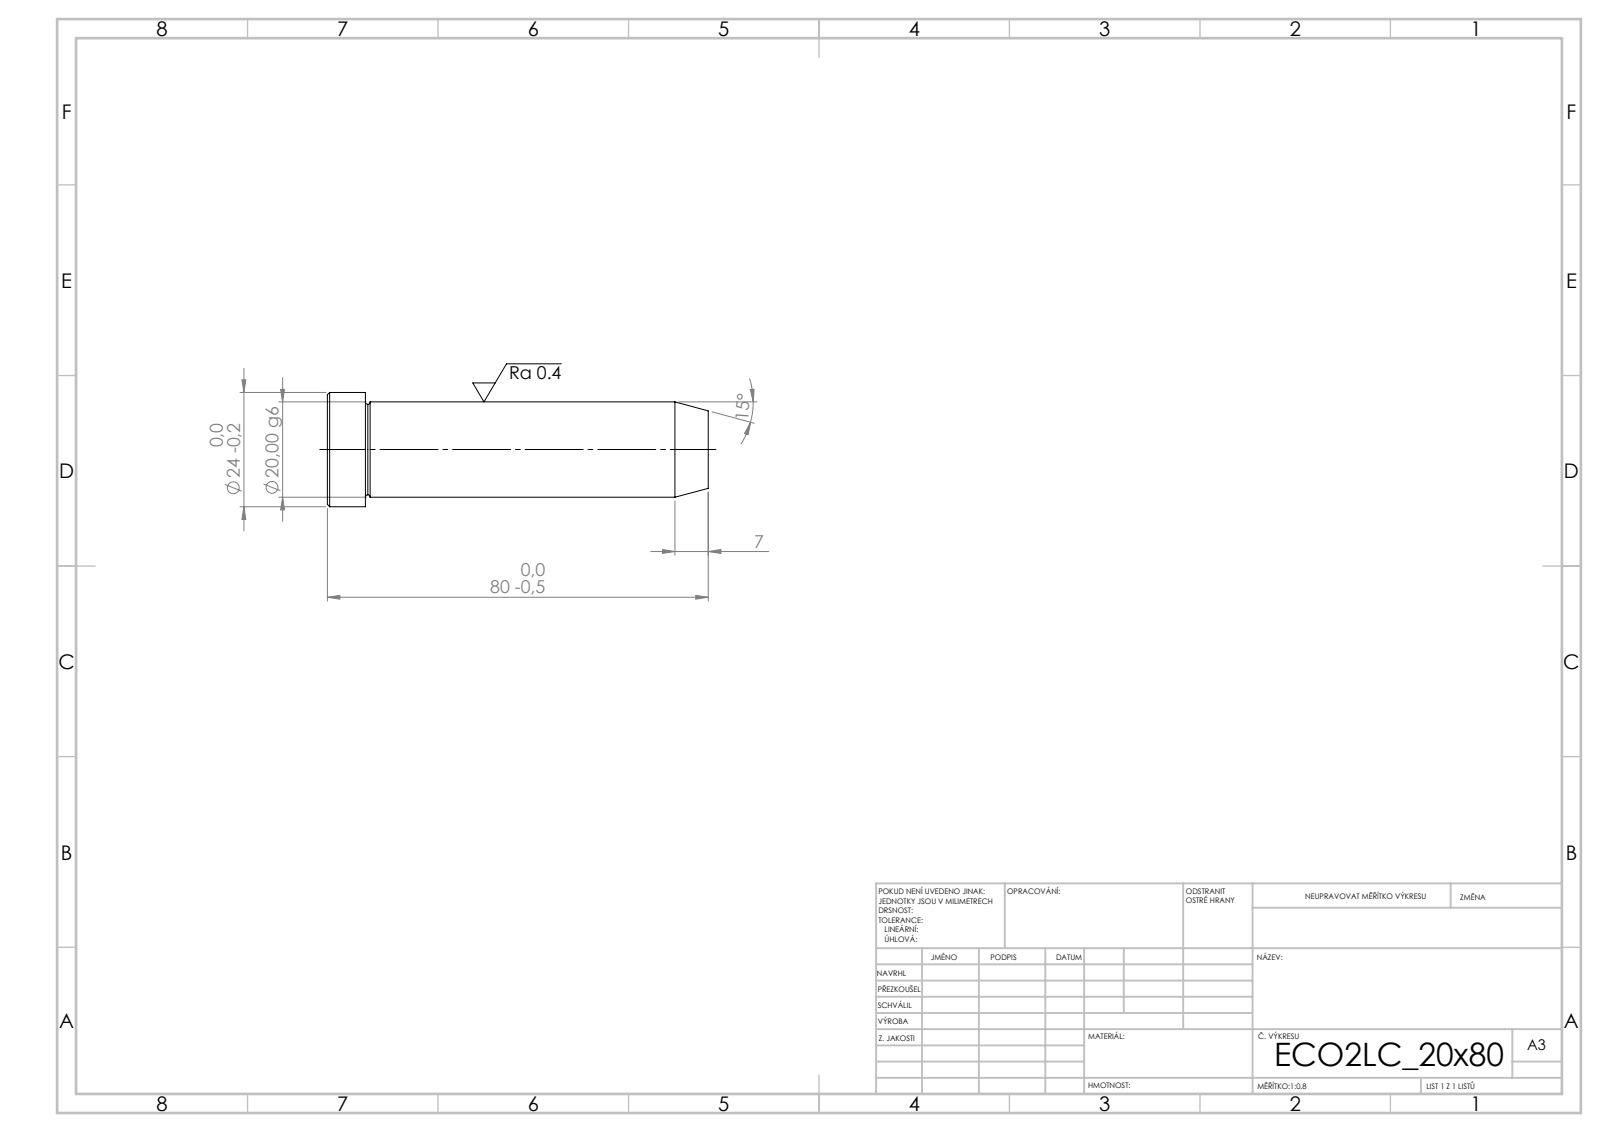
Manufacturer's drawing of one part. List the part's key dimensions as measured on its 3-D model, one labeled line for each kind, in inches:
STEP written by: SolidWorks 2019 (CONFIG_CONTROL_DESIGN)
Units: inches
Bodies: 1 solid, 15 faces (3 planar, 4 cylindrical, 8 other)
Overall size (bounding box): 3.15 × 0.945 × 0.945
Volume: 1.576 in³ · Surface area: 9.157 in²
Round bosses / shafts (diameter × count): ⌀0.945 ×1, ⌀0.787 ×1
Main face-to-face distances: 3.15, 2.835, 0.315
